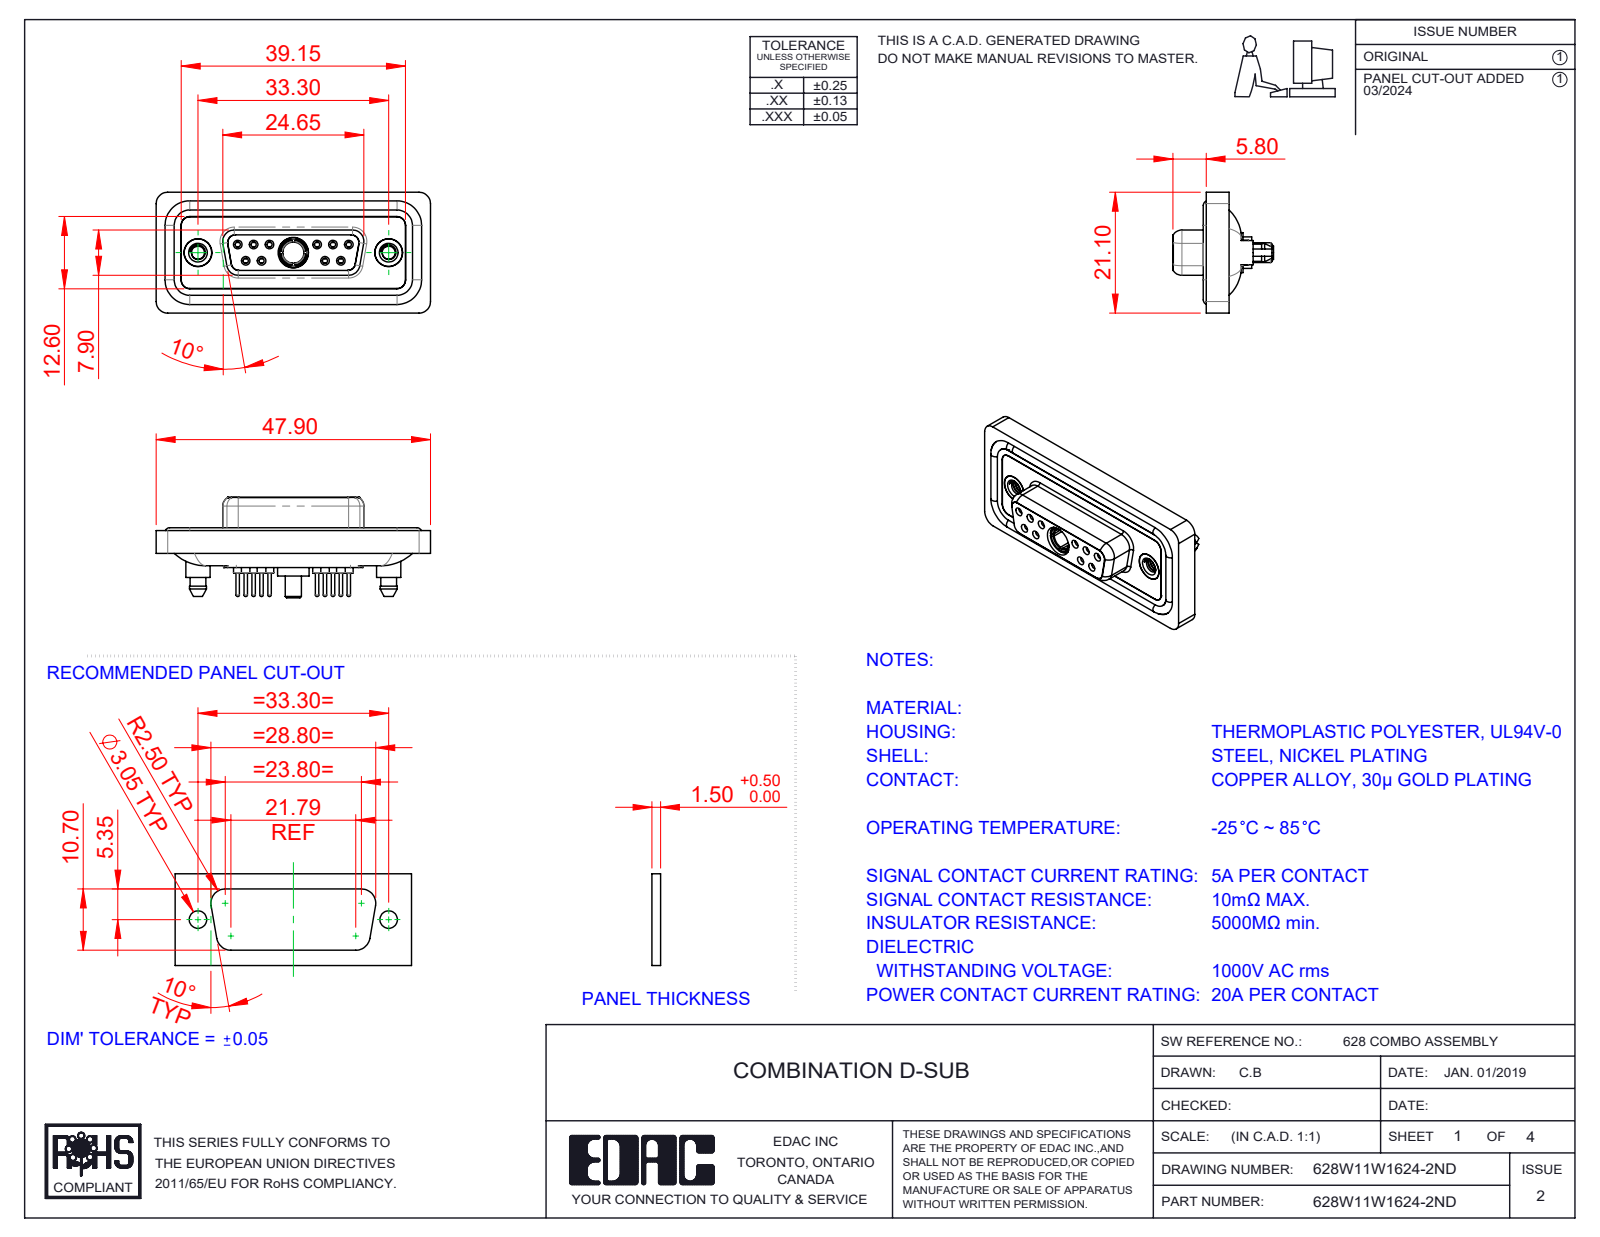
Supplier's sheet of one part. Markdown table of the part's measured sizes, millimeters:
| quantity | value |
| --- | --- |
| part name | 628Combo Waterproof Housing_15 Contacts; Power Socket_20A S; 628Combo Shell Rear_15 Contacts; 628W11W1624-2ND (+5 more) |
| STEP written by | SolidWorks 2023 (CONFIG_CONTROL_DESIGN) |
| units | millimeters |
| bodies | 19 solids, 1076 faces (300 planar, 449 cylindrical, 327 other) |
| overall size | 47.9 × 21.1 × 17.55 |
| volume | 6 262 mm³ |
| surface area | 10 371 mm² |
| round holes (diameter × count) | 0.9 × 10, 1.1 × 10, 1.5 × 10, 2 × 10, 1.7 × 6, 1.6 × 4, 4.85 × 3, 2.26 × 2, 4 × 2, 4.05 × 2, 5 × 2, 3.7 × 1 |
| round bosses / shafts (diameter × count) | 2.2 × 10, 1.6 × 10, 0.6 × 10, 5.4 × 2, 4.95 × 2, 4.8 × 2, 4.25 × 2, 5.5 × 1 |
| partial cylindrical surfaces (radius × count) | 1.5 × 24, 2 × 20, 1.35 × 12, 1.6 × 10, 0.25 × 4, 0.5 × 4, 0.6 × 4, 0.65 × 4 |
| main face-to-face distances | 0.4, 1.6, 1.8, 2.9, 0.5, 1.1, 5.65, 7.45, 6.6, 7.05 |
| hole center spacings | 3.16, 2.77, 13.85, 11.08, 16.62, 5.03, 5.04, 5.54 |
